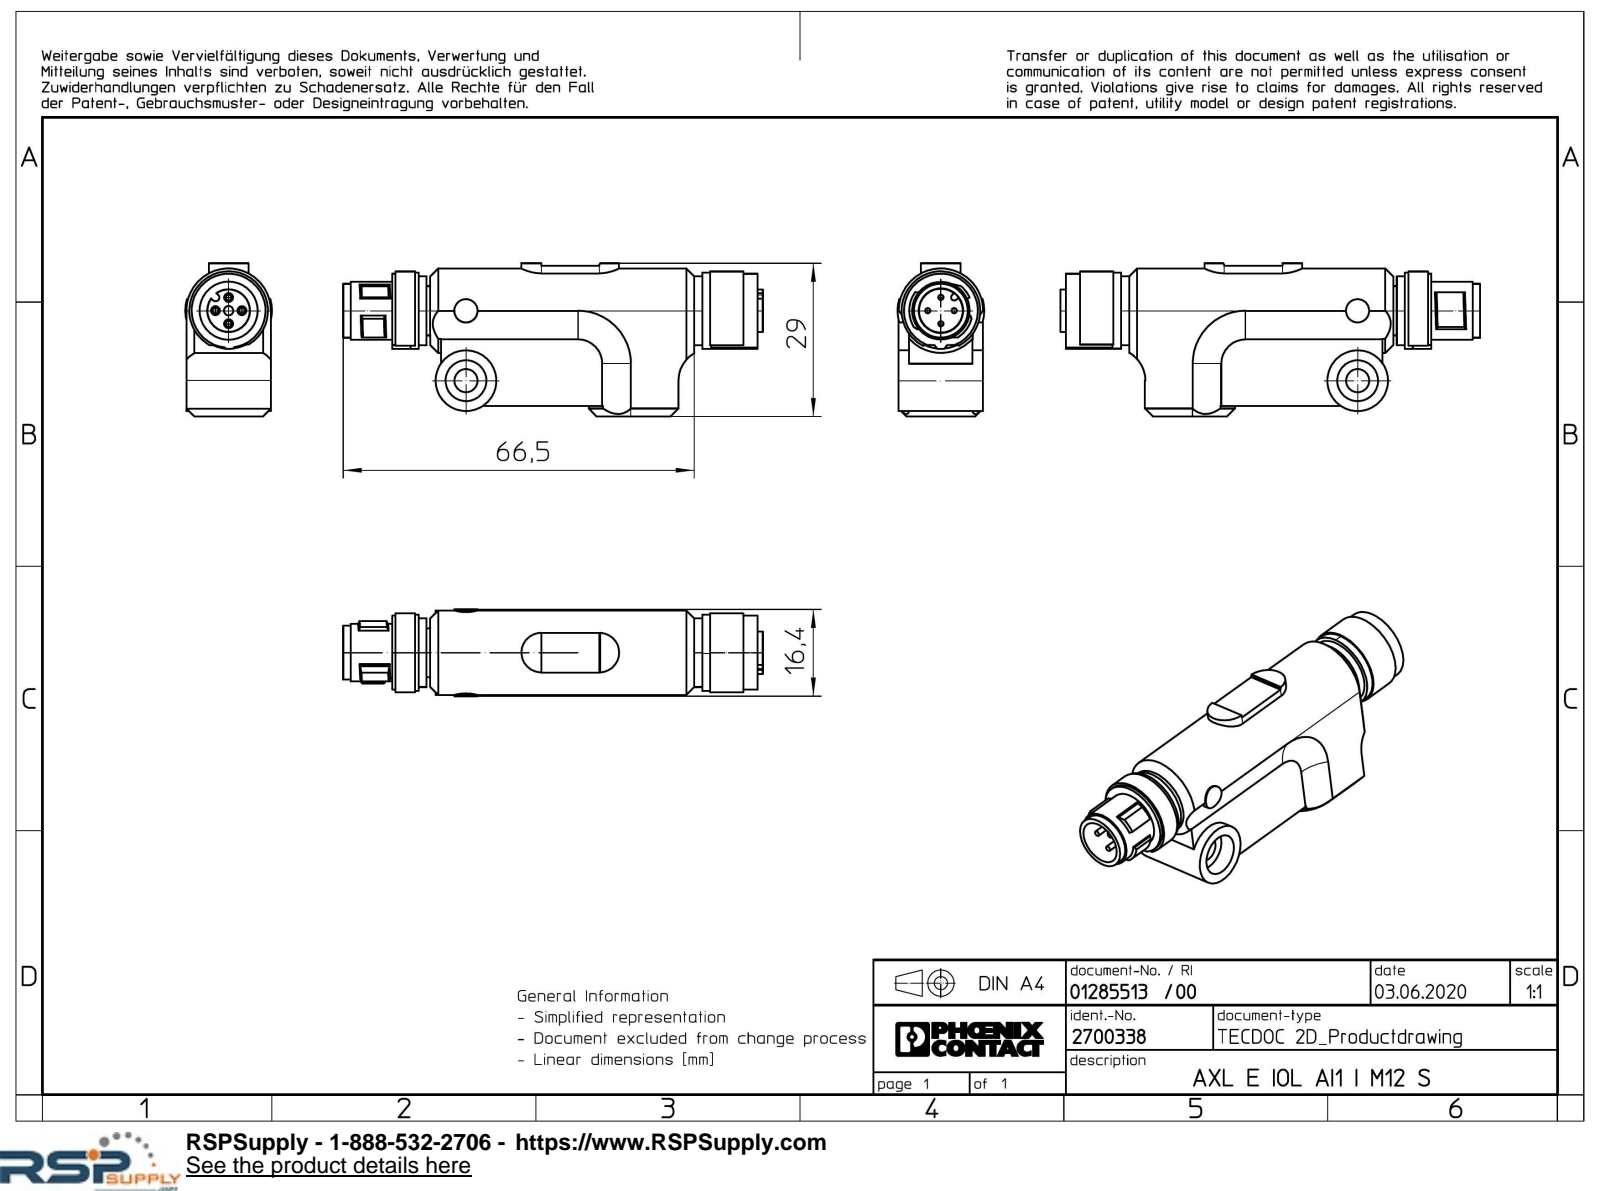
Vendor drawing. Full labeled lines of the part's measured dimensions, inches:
Part name (STEP PRODUCT): AXL_E_IOL_..._..._M12_S-select
STEP written by: Creo Elements/Direct Modeling 20.1A 29-Sep-2018 (C) Parametric Technology GmbH (AUTOMOTIVE_DESIGN)
Units: inches
Bodies: 1 solid, 171 faces (82 planar, 62 cylindrical, 27 other)
Overall size (bounding box): 3.13 × 1.141 × 0.646
Volume: 1.241 in³ · Surface area: 10.72 in²
Round holes (diameter × count): ⌀0.043 ×4, ⌀0.071 ×1, ⌀0.173 ×1, ⌀0.305 ×1, ⌀0.434 ×1
Round bosses / shafts (diameter × count): ⌀0.039 ×4, ⌀0.587 ×1, ⌀0.567 ×1, ⌀0.551 ×1, ⌀0.512 ×1, ⌀0.453 ×1, ⌀0.429 ×1, ⌀0.402 ×1
Partial cylindrical surfaces — rounded edges, fillets, slot ends (radius × count): R0.315 ×6, R0.148 ×2, R0.236 ×2, R0.024 ×1, R0.028 ×1, R0.323 ×1
Main face-to-face distances: 0.079, 0.551, 0.472, 0.63, 2.362, 0.106, 2.618, 1.043, 1.122, 0.028
Hole centre spacings: 0.098, 0.139, 0.197
